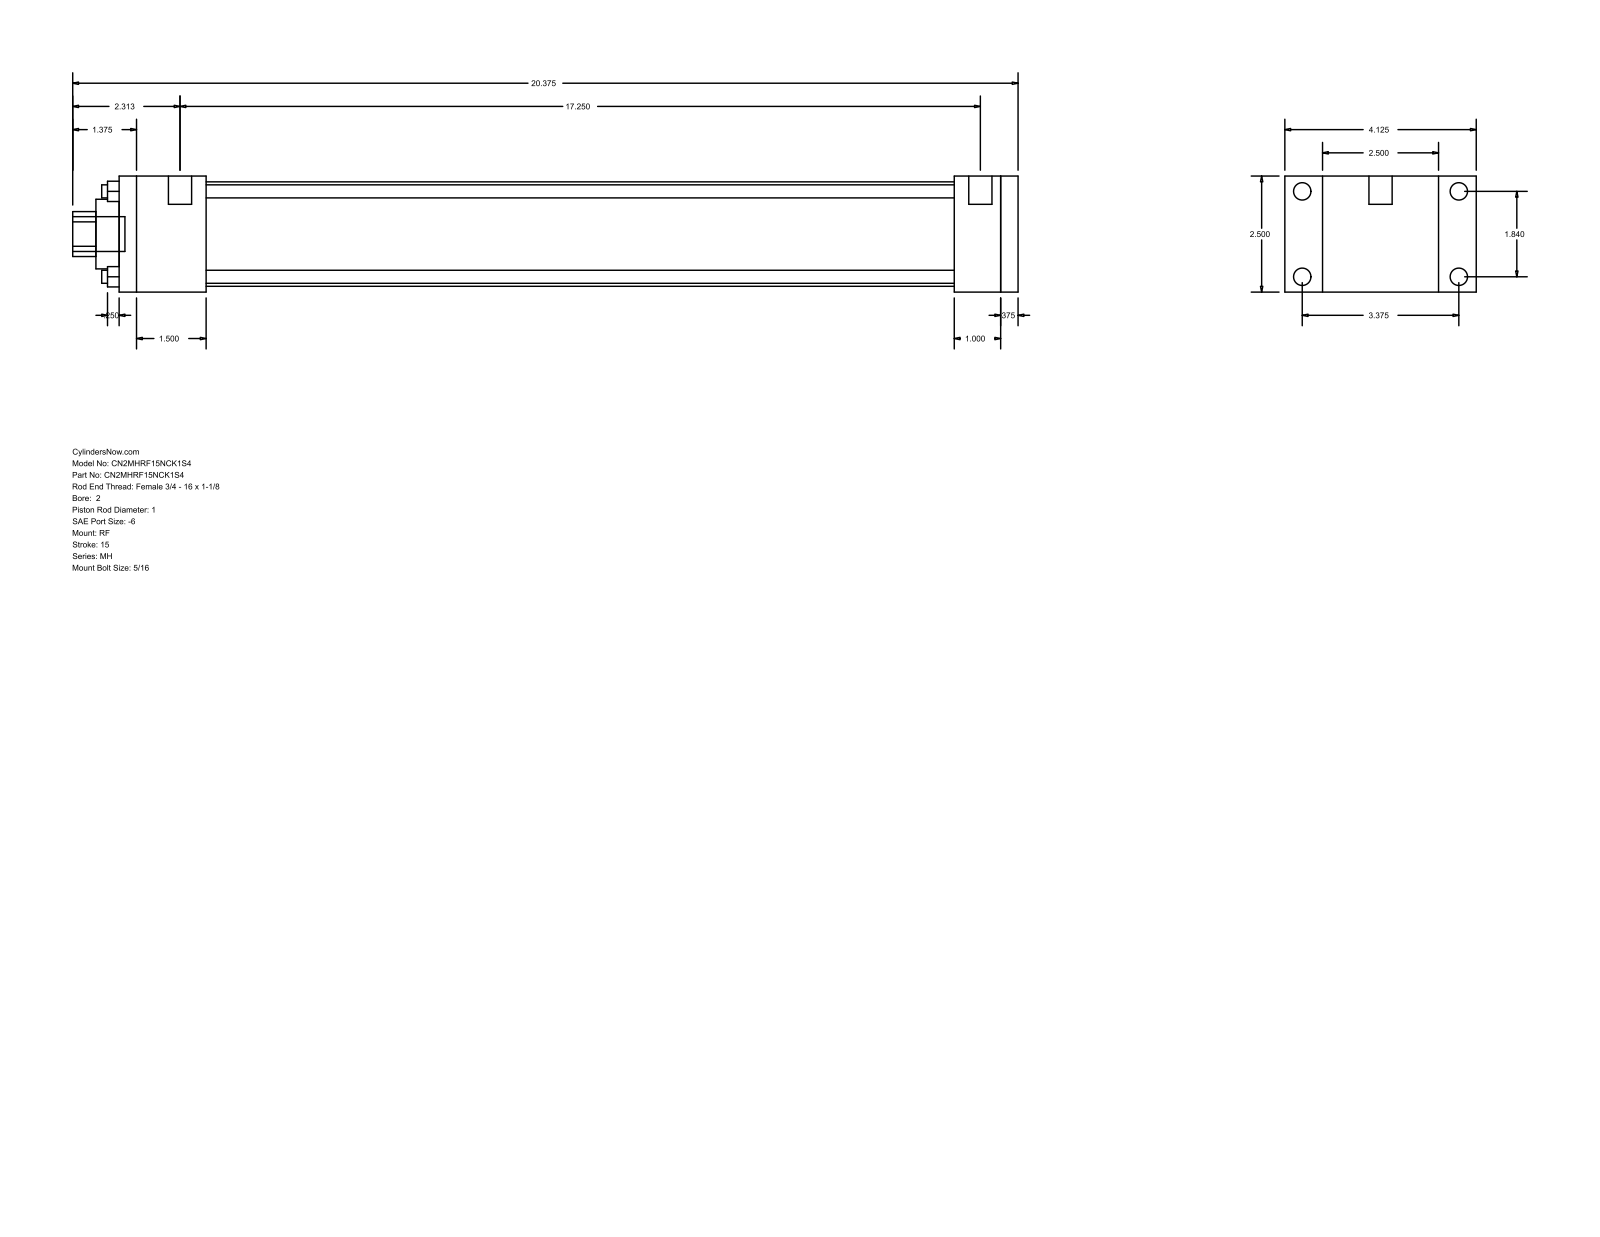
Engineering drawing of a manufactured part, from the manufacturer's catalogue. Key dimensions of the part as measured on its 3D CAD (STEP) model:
Part name (STEP PRODUCT): MH_RF__0200_1
STEP written by: GSSL Pune (CONFIG_CONTROL_DESIGN)
Units: millimetres
Bodies: 0 solids, 92 faces (64 planar, 28 cylindrical, 0 other)
Overall size (bounding box): 517.52 × 104.78 × 63.5
Round holes (diameter × count): ⌀7.14 ×4, ⌀25.4 ×1, ⌀38.1 ×1, ⌀57.15 ×1
Round bosses / shafts (diameter × count): ⌀9.53 ×4, ⌀5.56 ×4, ⌀12.7 ×2, ⌀19.05 ×1
Partial cylindrical surfaces — rounded edges, fillets, slot ends (radius × count): R12.29 ×1
Main face-to-face distances: 63.5, 9.52, 492.12, 482.6, 20.64, 25.4, 47.63, 457.2, 409.57, 434.97
Hole centre spacings: 33.05, 46.74, 66.1
